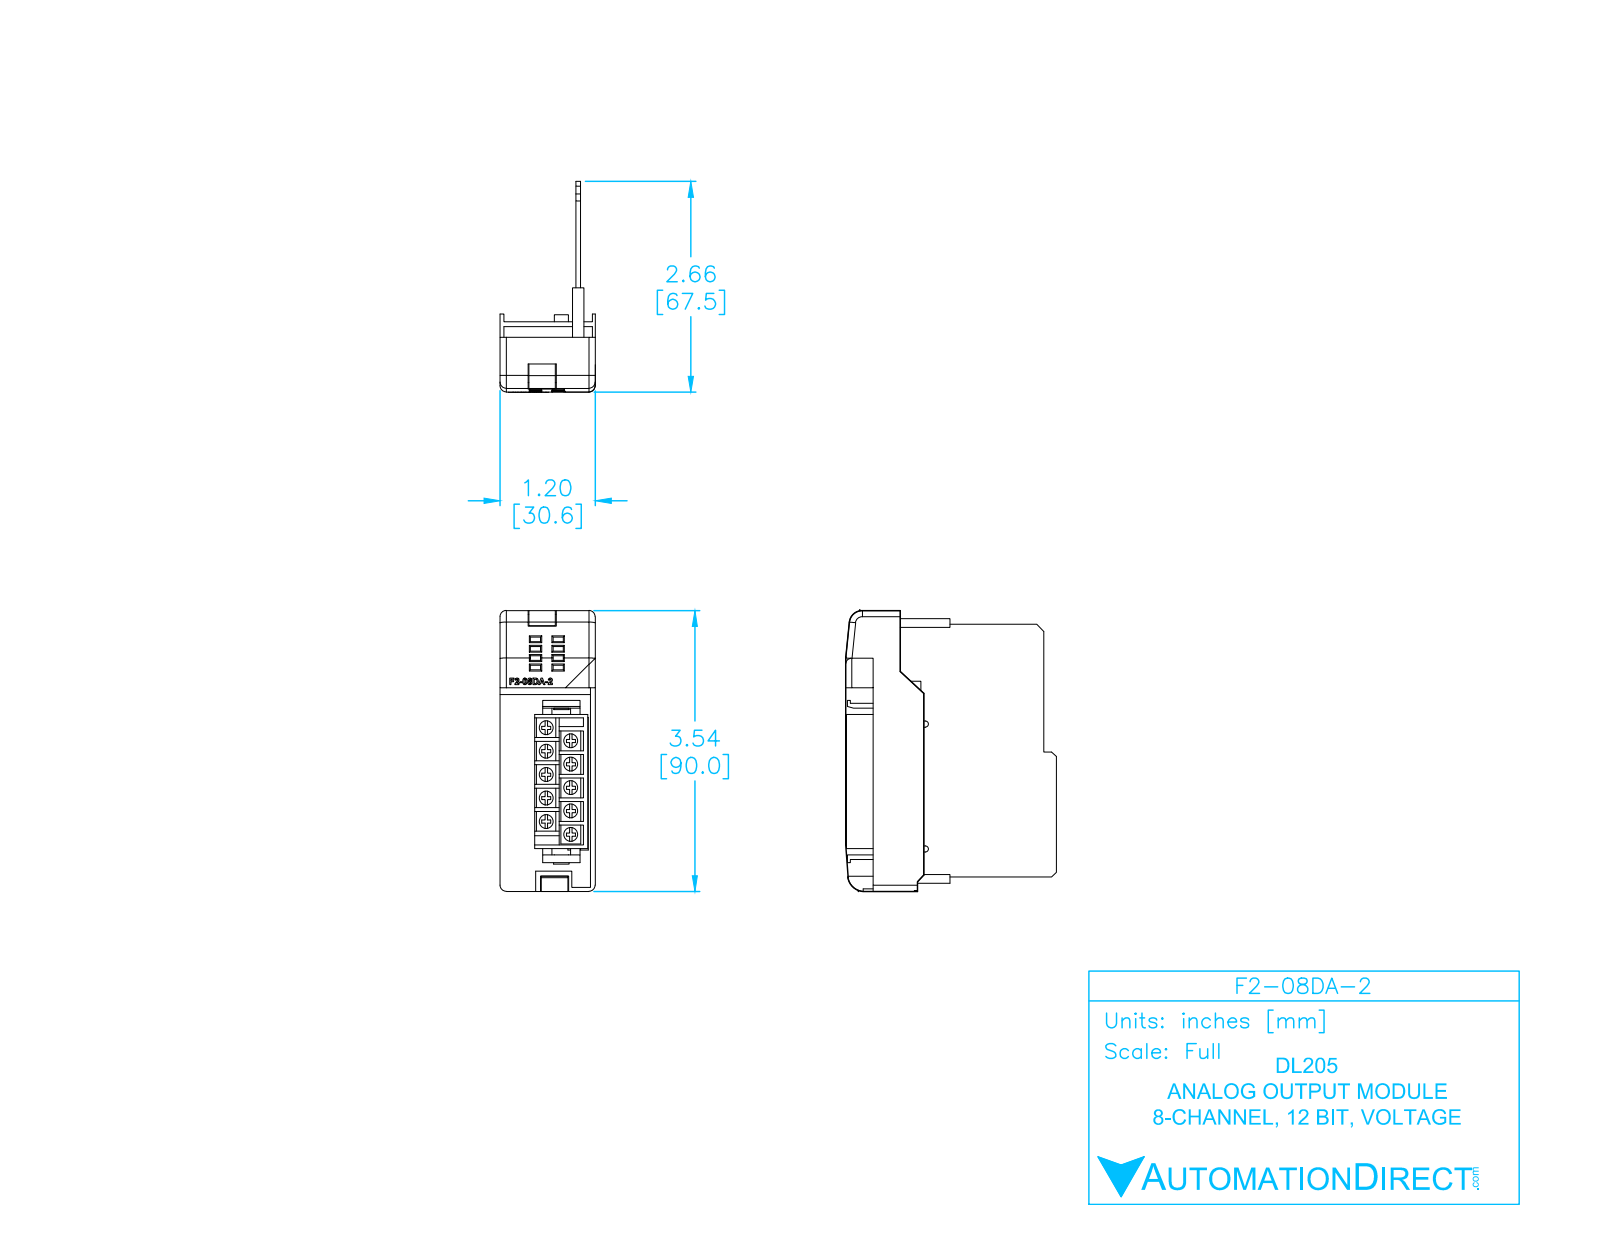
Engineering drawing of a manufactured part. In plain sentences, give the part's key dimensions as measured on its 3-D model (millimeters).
The part is named "F2-08DA-2_ModuleCase_light_NEW". Its 3-D file was written by "SolidWorks 2009 (AUTOMOTIVE_DESIGN)". It is 6 solids with 586 faces: 411 planar, 75 cylindrical and 100 other. Overall it measures 90 by 69.22 by 30.55 millimeters. Its volume is 25 405 cubic millimeters and its surface area 28 580 square millimeters. Round bosses or shafts: 10 of diameter 4.5. Partial cylindrical surfaces (rounded edges, fillets, slot ends): 16 of radius 0.35, 9 of radius 2, 2 of radius 0.25, 2 of radius 1, 2 of radius 1.25, 1 of radius 4.12, 1 of radius 5.39. The main face-to-face distances are 1.5, 4.72, 6.22, 3.62, 2.12, 2.6, 3.22, 1.1, 8.14, 24.28.
